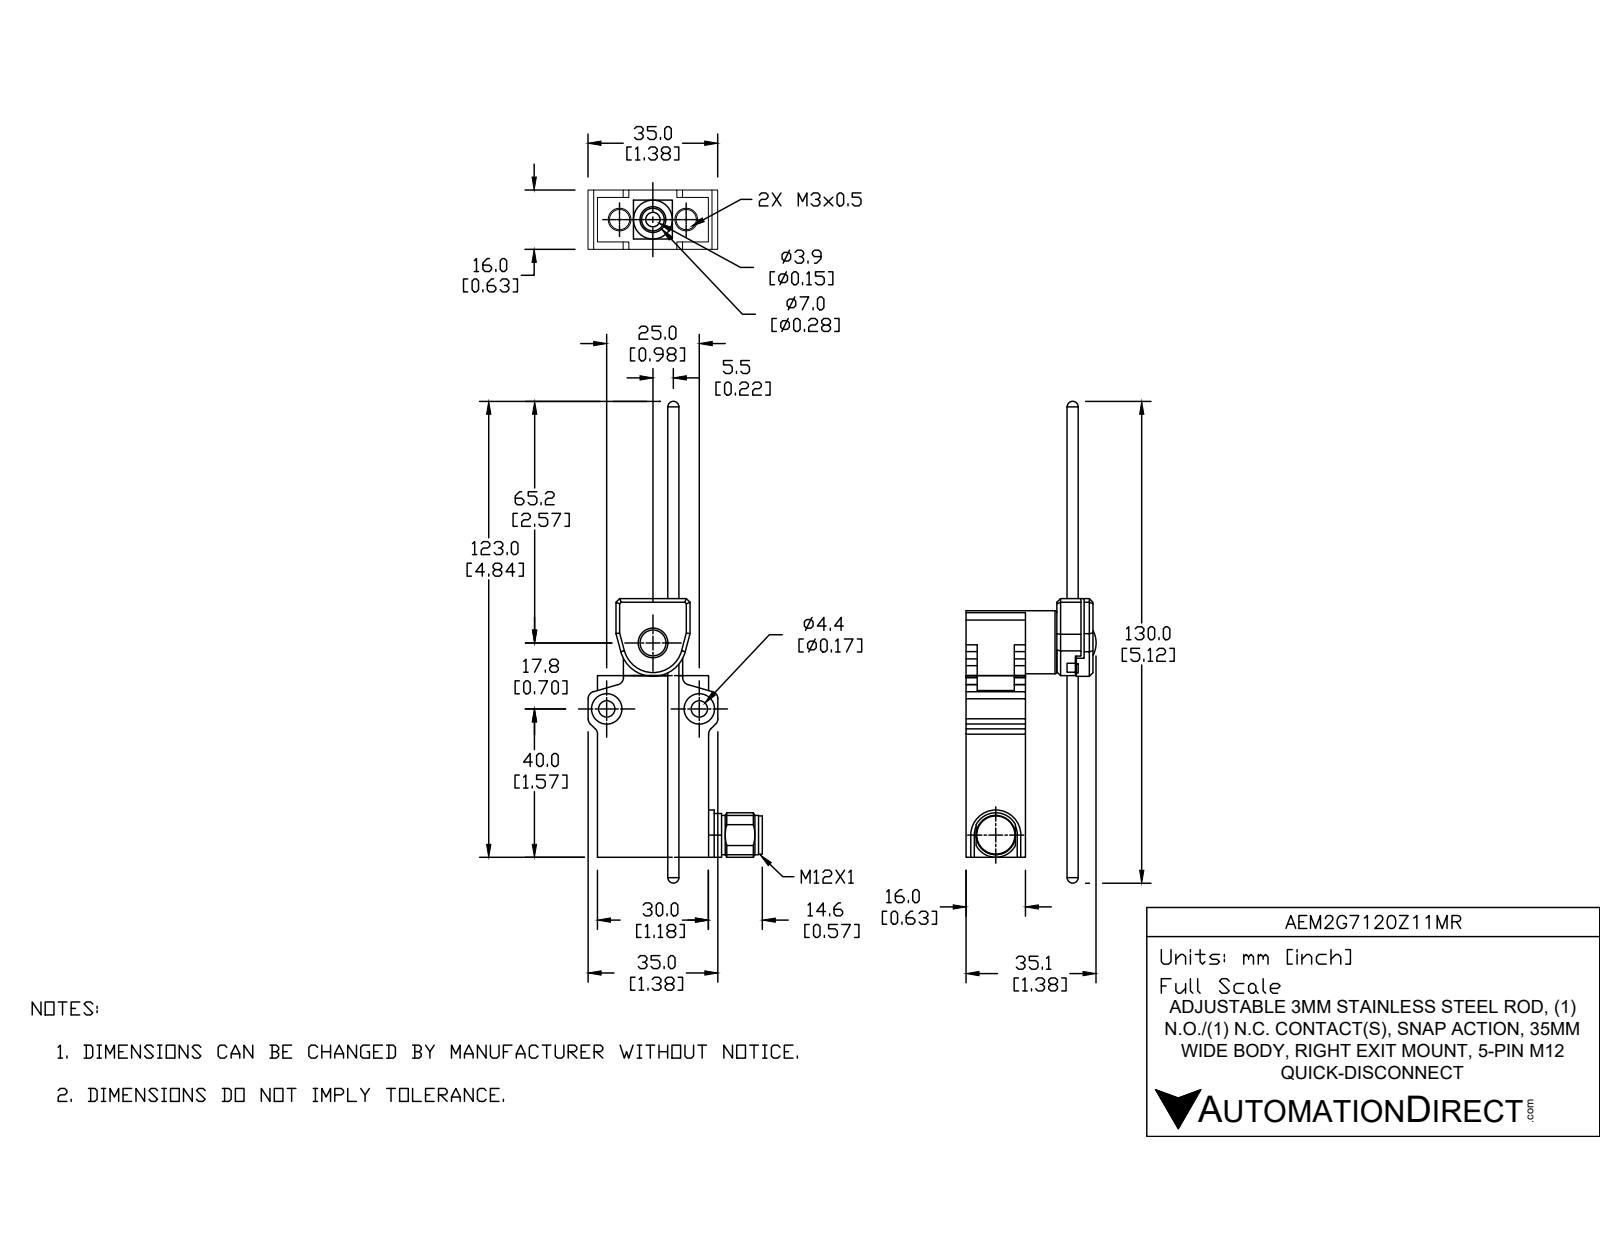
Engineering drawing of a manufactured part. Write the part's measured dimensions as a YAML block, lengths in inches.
part_name: "AEM2G7120Z11MR"
step_written_by: "SolidWorks 2019 (AUTOMOTIVE_DESIGN)"
units: inches
bodies: {solids: 7, faces: 239, planar: 141, cylindrical: 61, other: 37}
overall_size: [6.924, 1.831, 1.366]
volume: 2.085
surface_area: 21.23
round_holes:
  - {diameter: 0.118, count: 3}
  - {diameter: 0.173, count: 2}
  - {diameter: 0.323, count: 2}
  - {diameter: 0.197, count: 1}
  - {diameter: 0.315, count: 1}
round_bosses_or_shafts:
  - {diameter: 0.622, count: 1}
  - {diameter: 0.472, count: 1}
  - {diameter: 0.417, count: 1}
  - {diameter: 0.406, count: 1}
  - {diameter: 0.276, count: 1}
  - {diameter: 0.138, count: 1}
partial_cylinders:
  - {radius: 0.079, count: 8}
  - {radius: 0.059, count: 1}
  - {radius: 0.173, count: 1}
  - {radius: 0.256, count: 1}
  - {radius: 0.26, count: 1}
  - {radius: 0.354, count: 1}
face_to_face_distances: [0.63, 1.181, 2.047, 0.169, 0.472, 0.28, 0.902, 0.988, 1, 0.697]
hole_center_spacings: [0.863, 0.748, 0.857, 0.984, 1.029]
